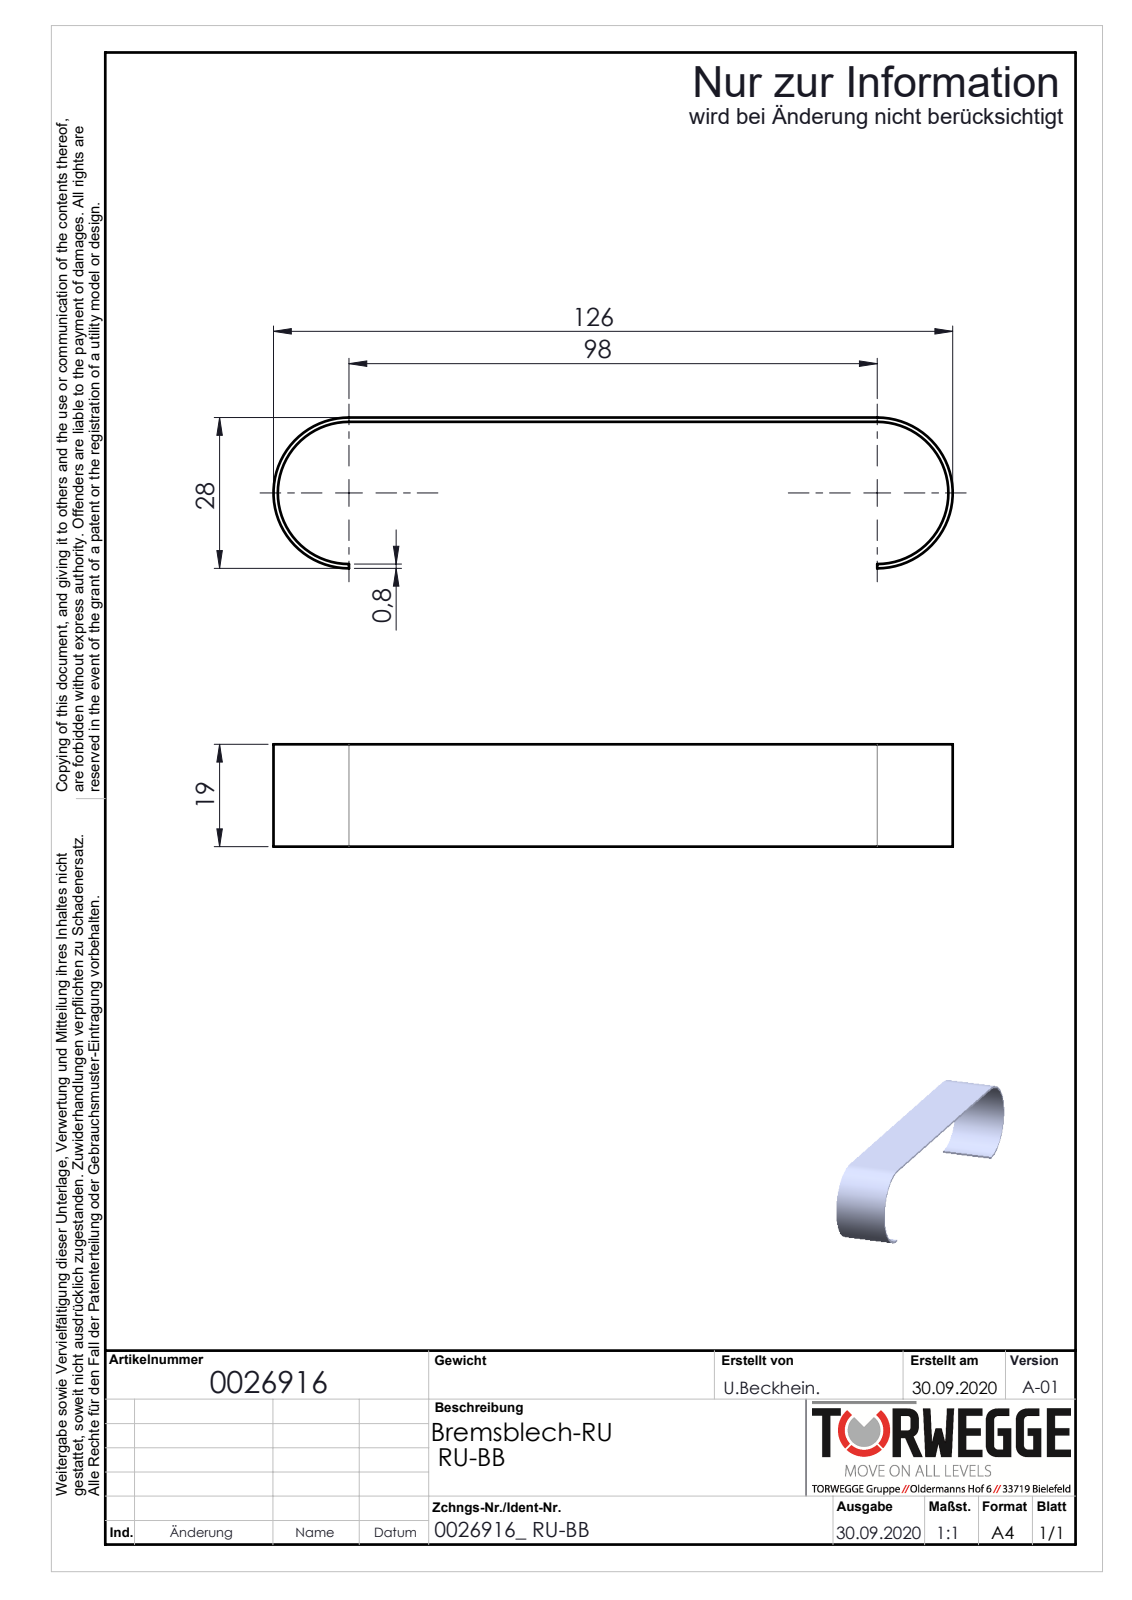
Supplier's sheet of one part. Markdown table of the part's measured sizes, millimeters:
| quantity | value |
| --- | --- |
| part name | 0026916 |
| STEP written by | SolidWorks 2018 (AUTOMOTIVE_DESIGN) |
| units | millimeters |
| bodies | 1 solid, 12 faces (6 planar, 6 cylindrical, 0 other) |
| overall size | 126 × 28 × 19 |
| volume | 2 788 mm³ |
| surface area | 7 295 mm² |
| partial cylindrical surfaces (radius × count) | 13.2 × 2, 14 × 2 |
| main face-to-face distances | 0.8, 19, 98 |
